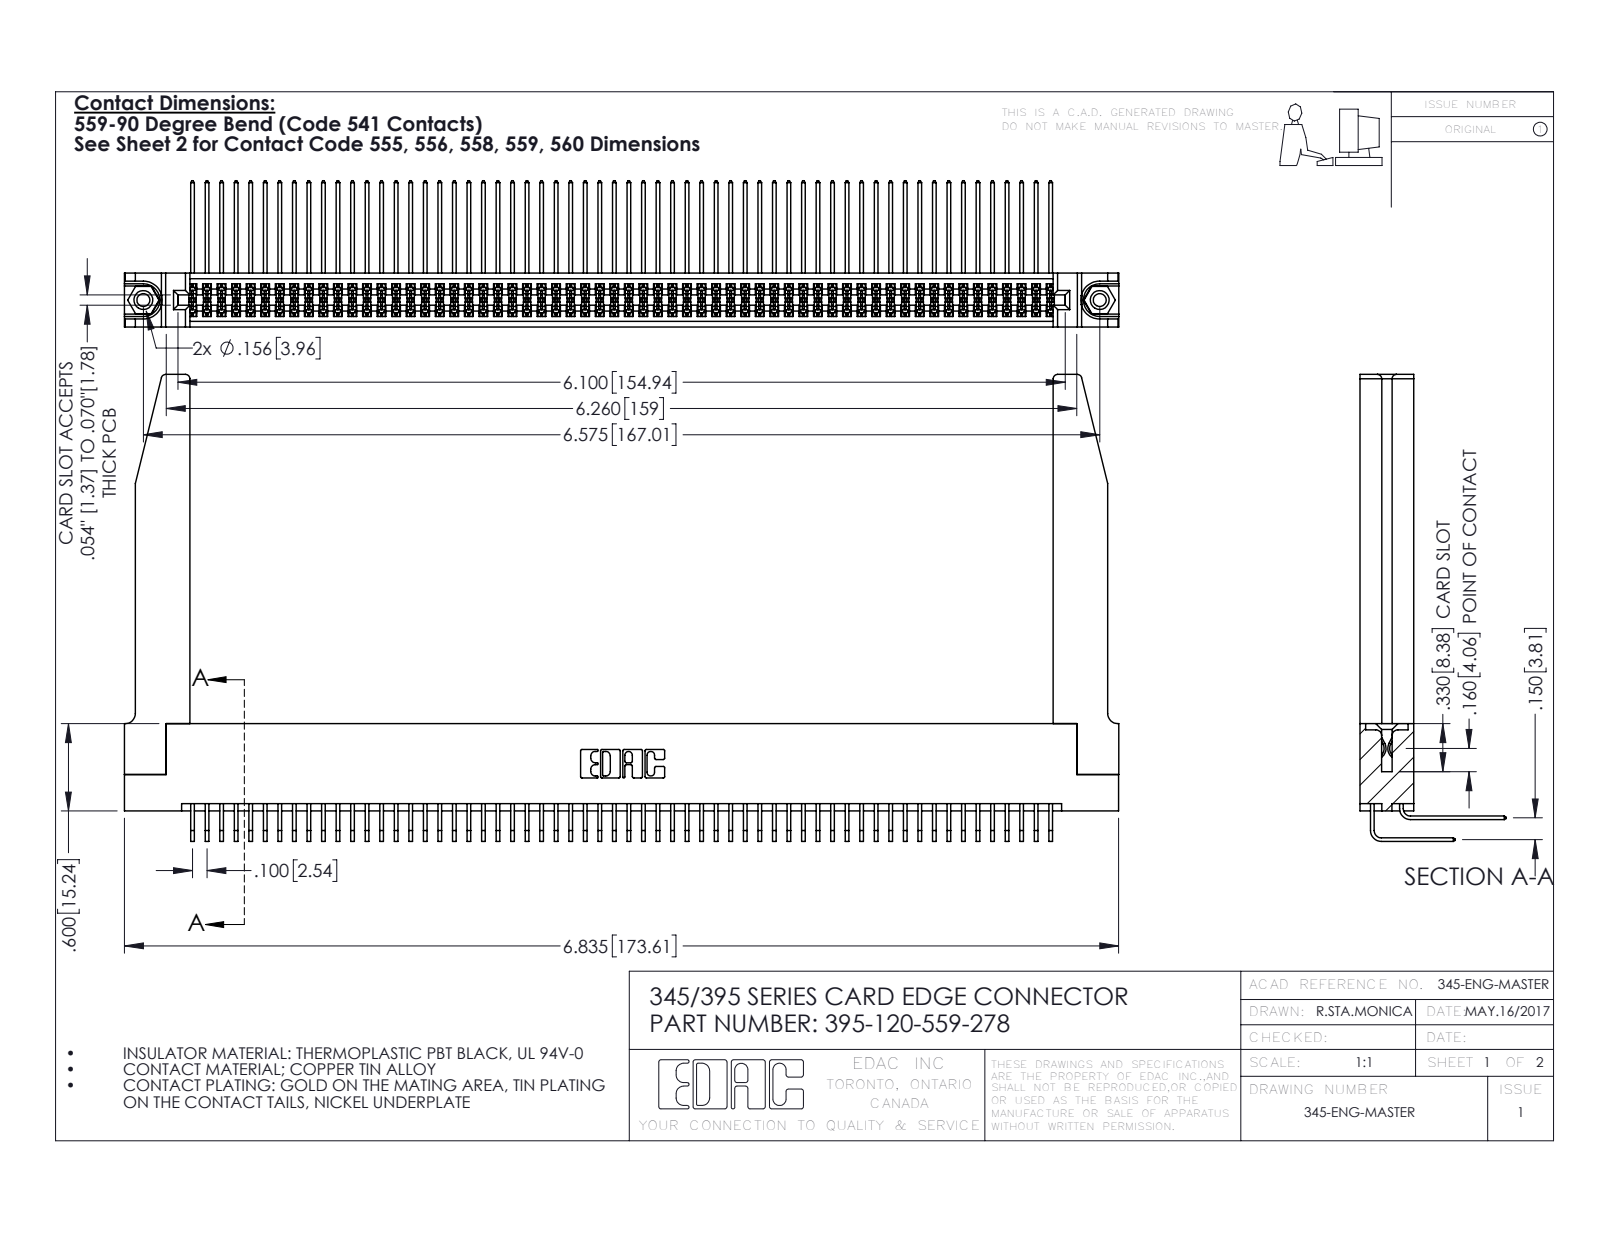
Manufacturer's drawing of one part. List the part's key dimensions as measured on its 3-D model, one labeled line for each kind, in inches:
Part name (STEP PRODUCT): 345-292-001_559 Tail - 2; 345-220-078_345-220-078; 395-120-559-278; 345 Part_Flush Mounting Lugs - 0.156 Dia-TH (+2 more)
STEP written by: SolidWorks 2016 (CONFIG_CONTROL_DESIGN)
Units: inches
Bodies: 125 solids, 6600 faces (4422 planar, 2126 cylindrical, 52 other)
Overall size (bounding box): 6.836 × 3.209 × 1.005
Volume: 1.556 in³ · Surface area: 56.8 in²
Round holes (diameter × count): ⌀0.089 ×2, ⌀0.125 ×2, ⌀0.156 ×2, ⌀0.064 ×1
Round bosses / shafts (diameter × count): ⌀0.155 ×2
Partial cylindrical surfaces — rounded edges, fillets, slot ends (radius × count): R0.006 ×180, R0.01 ×22, R0.03 ×8, R0.007 ×6, R0.031 ×6, R0.026 ×3, R0.014 ×2, R0.019 ×2
Main face-to-face distances: 0.072, 0.298, 0.37, 0.2, 0.098, 0.272, 0.025, 0.225, 0.175, 0.15
Hole centre spacings: 0.27, 6.339, 6.575
